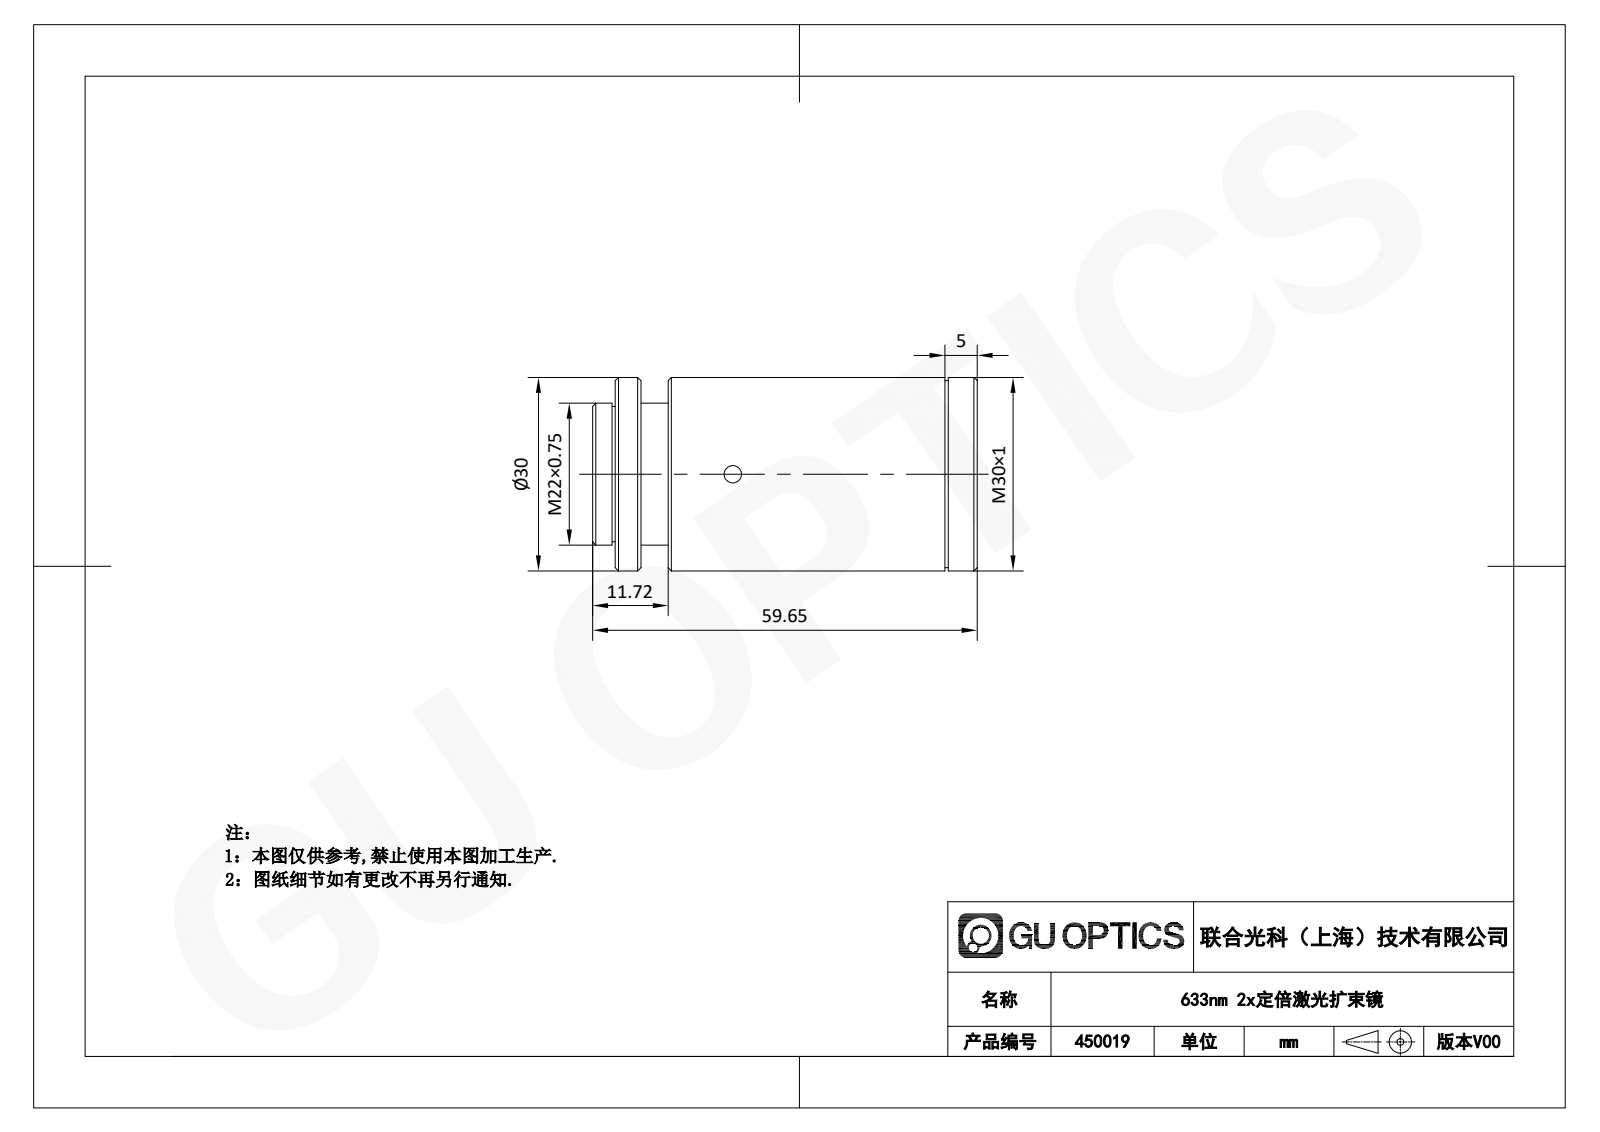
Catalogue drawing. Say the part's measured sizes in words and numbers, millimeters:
The part is named "450019". Its 3-D file was written by "SolidWorks 2020 (CONFIG_CONTROL_DESIGN)". It is 1 solid with 44 faces: 12 planar, 22 cylindrical and 10 other. Overall it measures 59.65 by 30 by 30 millimeters. Its volume is 38 626 cubic millimeters and its surface area 8 343 square millimeters. Round holes: 1 of diameter 2, 1 of diameter 8, 1 of diameter 18, 1 of diameter 20. Round bosses or shafts: 1 of diameter 30, 1 of diameter 29, 1 of diameter 22, 1 of diameter 21. The main face-to-face distances are 2, 57.65, 1, 56.15, 1.5, 52.15, 2.5, 54.15, 3.5, 59.65.
